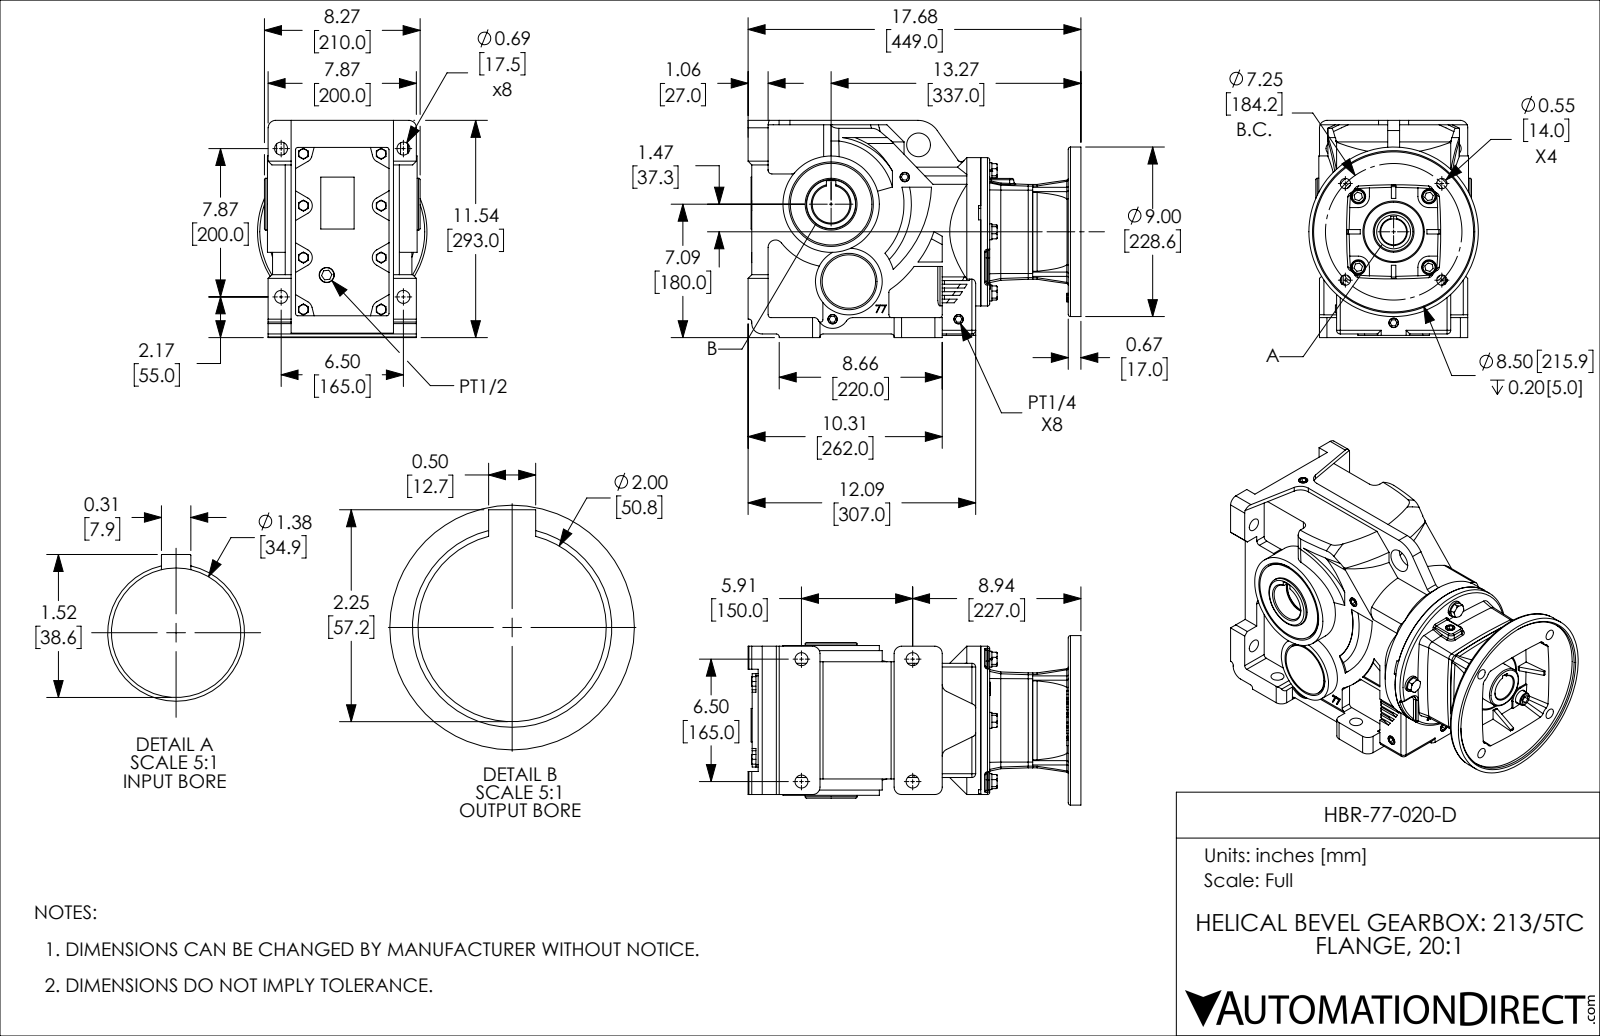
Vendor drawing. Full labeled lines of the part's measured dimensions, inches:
Part name (STEP PRODUCT): HBR-77-020-D
STEP written by: SolidWorks 2018 (AUTOMOTIVE_DESIGN)
Units: inches
Bodies: 43 solids, 1785 faces (759 planar, 598 cylindrical, 428 other)
Overall size (bounding box): 17.677 × 11.535 × 9
Volume: 374.3 in³ · Surface area: 1 991 in²
Round holes (diameter × count): ⌀0.268 ×8, ⌀0.354 ×8, ⌀0.689 ×8, ⌀0.335 ×4, ⌀0.402 ×4, ⌀0.433 ×4, ⌀0.472 ×4, ⌀0.48 ×4, ⌀0.512 ×4, ⌀0.551 ×4, ⌀0.787 ×4, ⌀0.438 ×3
Round bosses / shafts (diameter × count): ⌀0.315 ×8, ⌀0.846 ×4, ⌀0.709 ×4, ⌀0.394 ×4, ⌀5.118 ×2, ⌀0.827 ×2, ⌀9 ×1, ⌀7.874 ×1
Partial cylindrical surfaces — rounded edges, fillets, slot ends (radius × count): R0.394 ×37, R0.079 ×16, R0.591 ×15, R0.472 ×14, R0.197 ×12, R0.315 ×12, R0.118 ×9, R0.236 ×9
Main face-to-face distances: 0.236, 0.472, 0.315, 4.961, 0.787, 0.276, 5.748, 5.276, 0.512, 0.551
Hole centre spacings: 2.325, 5.461, 2.653, 2.756, 4.495, 4.968, 6.352, 6.496
